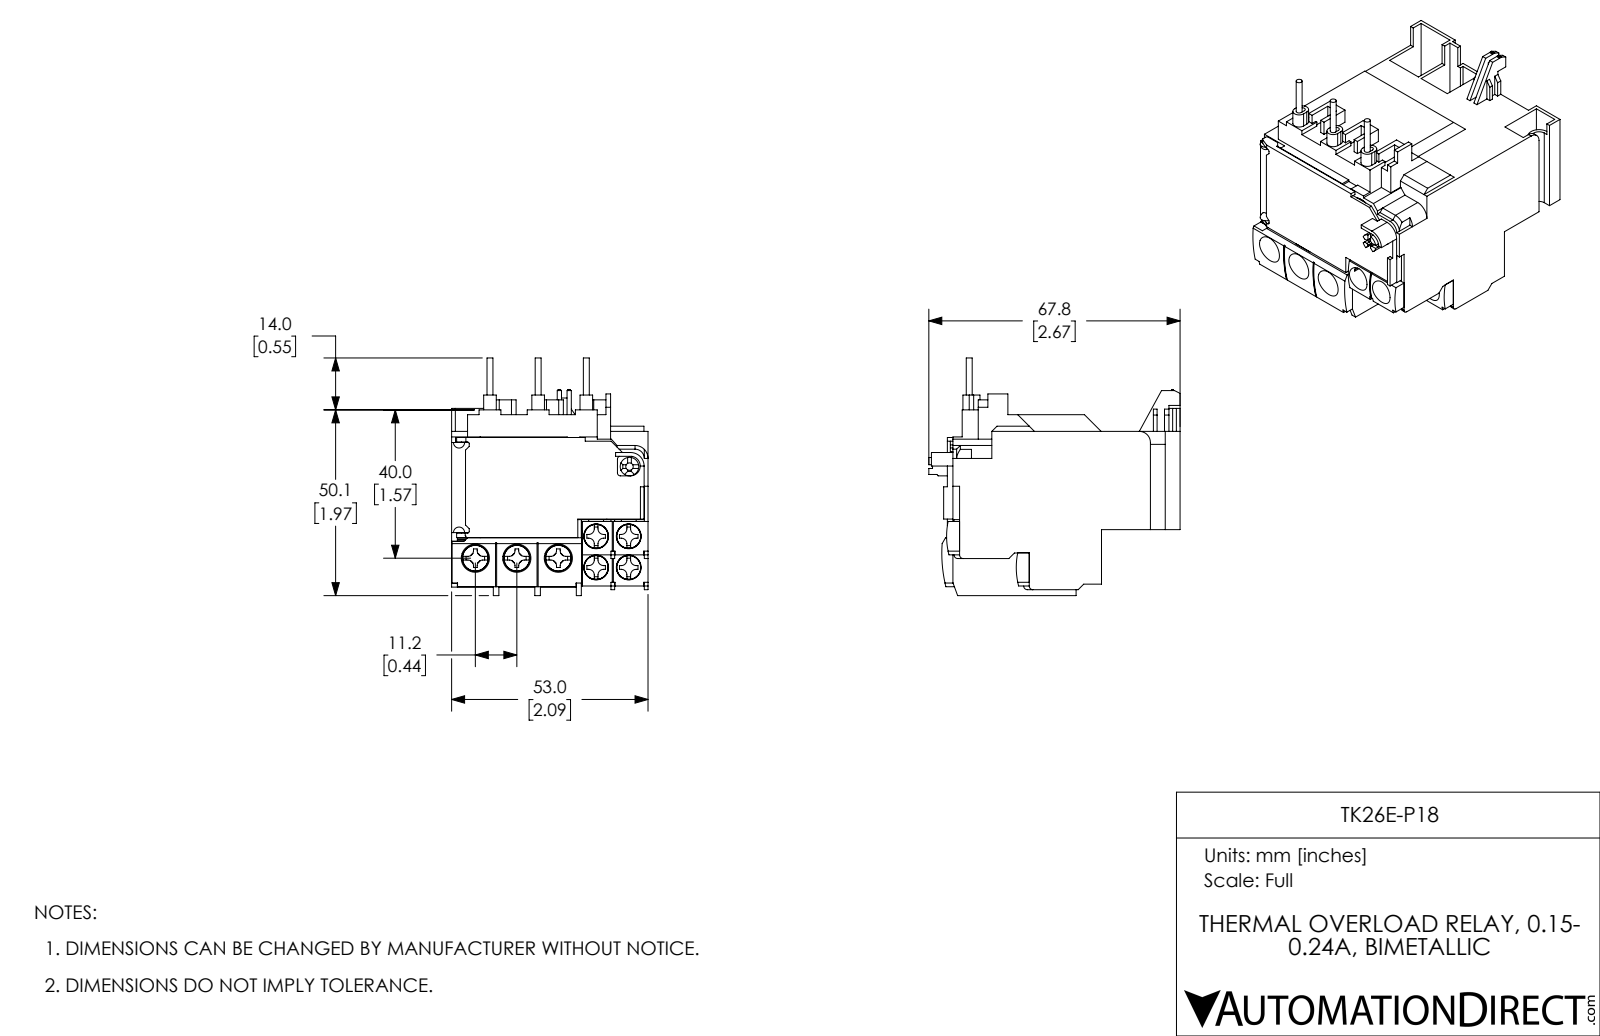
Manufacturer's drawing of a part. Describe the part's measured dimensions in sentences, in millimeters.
The part is named "TK26E-P18". Its 3-D file was written by "SolidWorks 2017 (AUTOMOTIVE_DESIGN)". It is 38 solids with 1480 faces: 1225 planar, 220 cylindrical and 35 other. Overall it measures 67.8 by 64.1 by 53 millimeters. Its volume is 99 940 cubic millimeters and its surface area 38 810 square millimeters. Round holes: 4 of diameter 3.5, 4 of diameter 3.6, 4 of diameter 6.7, 3 of diameter 4, 3 of diameter 4.1, 3 of diameter 7.6, 1 of diameter 1, 1 of diameter 2, 1 of diameter 5, 1 of diameter 11. Round bosses or shafts: 4 of diameter 6.6, 3 of diameter 1.6, 1 of diameter 6. Partial cylindrical surfaces (rounded edges, fillets, slot ends): 28 of radius 1.5, 8 of radius 1, 6 of radius 0.5, 6 of radius 1.7, 5 of radius 0.8, 4 of radius 1.2, 4 of radius 4.3, 3 of radius 4.8. The main face-to-face distances are 1, 9, 1.5, 12, 53, 2, 10, 11, 8.7, 0.7. The hole center spacings are 8.4, 8.8, 11.2, 12.2, 9.6, 10.5, 11.8, 18.8.
